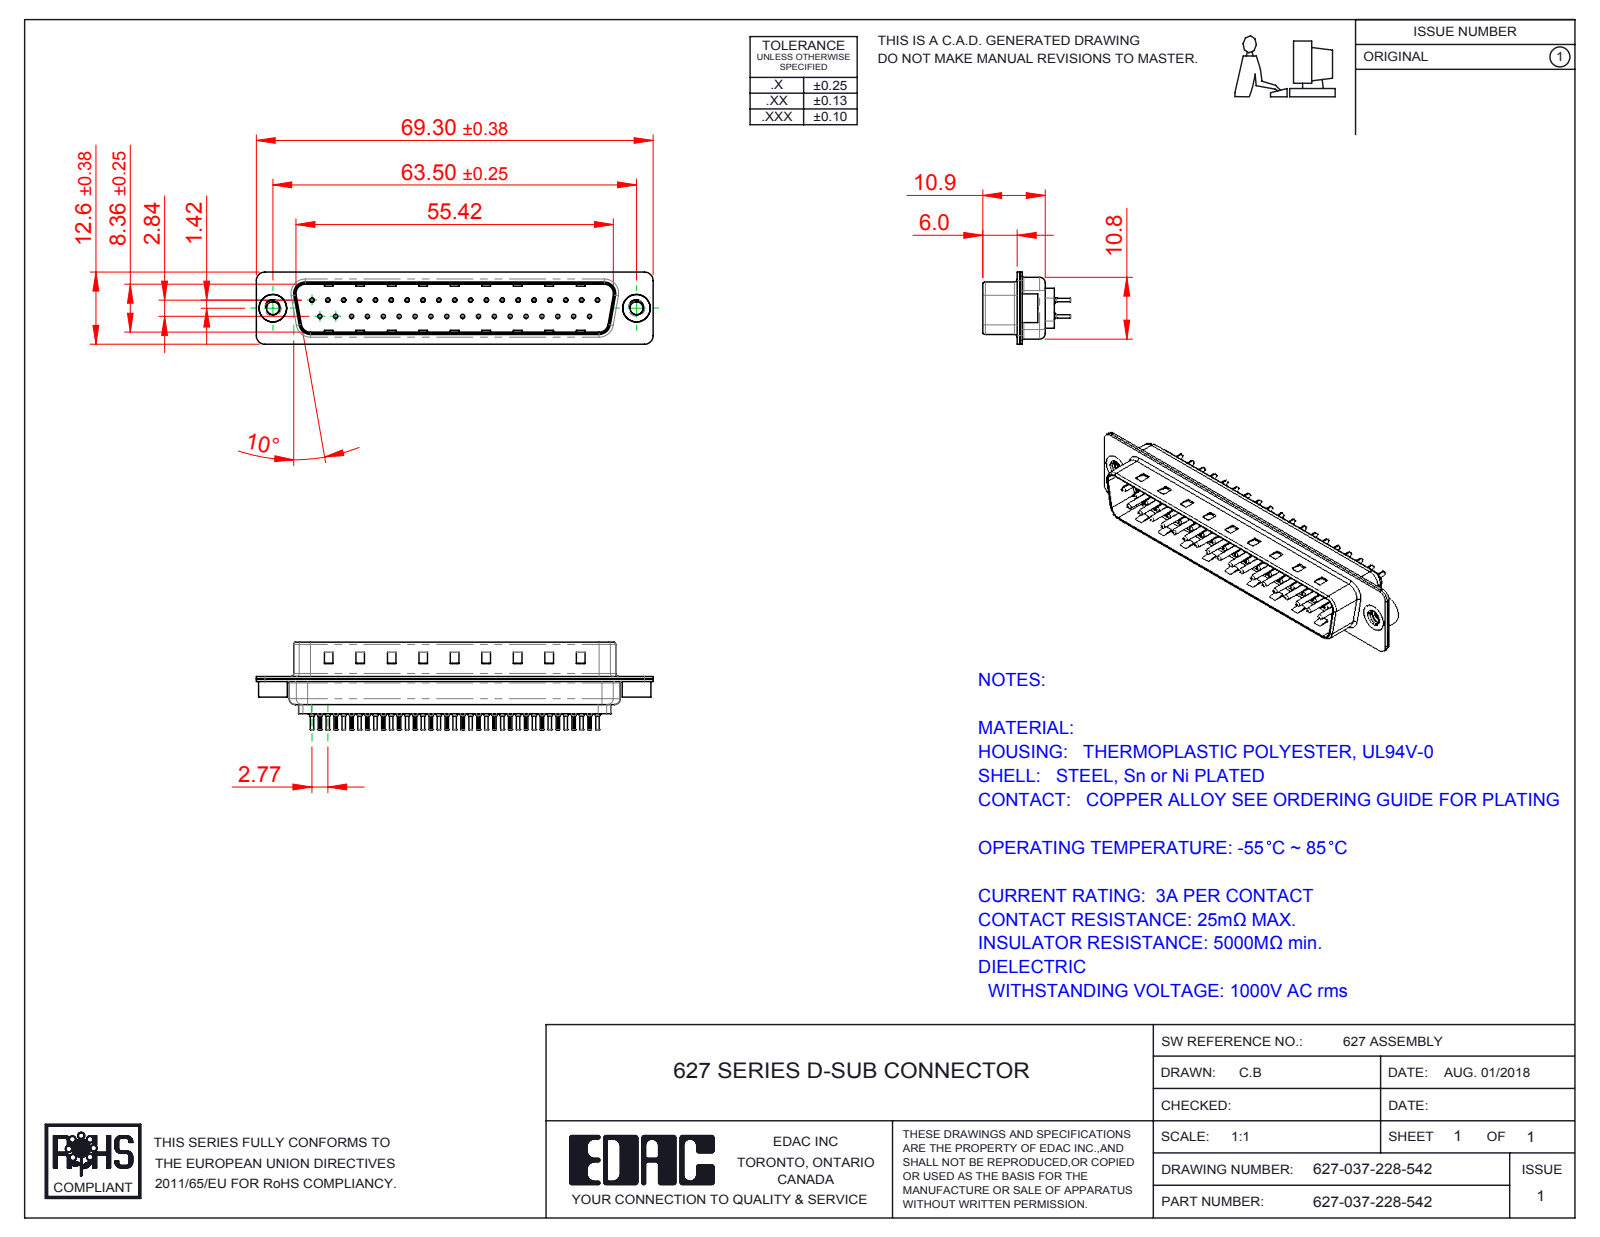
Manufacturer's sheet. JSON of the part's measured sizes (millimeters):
{"part_name": "627 Contact Row 2_28L; 627 Contact Row 1_28L; 627 4-40 Threaded Rivet; 627 Shell Rear_37 Contacts (+3 more)", "step_written_by": "SolidWorks 2016 (CONFIG_CONTROL_DESIGN)", "units": "millimeters", "bodies": {"solids": 42, "faces": 4038, "planar": 1091, "cylindrical": 1510, "other": 1437}, "overall_size": [69.3, 15.3, 12.6], "volume_mm3": 3685, "surface_area_mm2": 10474, "round_holes": [[0.2, 37], [0.35, 37], [1.1, 37], [1.6, 37], [2.26, 2], [4, 2], [4.8, 2]], "round_bosses_or_shafts": [[2, 37], [1.5, 37], [0.75, 37], [0.6, 37], [5, 2], [4.9, 2]], "partial_cylinders_radius": [[0.1, 74], [1.5, 16], [2, 12], [0.5, 8], [1.6, 8], [0.25, 4], [0.6, 4], [0.65, 4]], "face_to_face_distances": [0.4, 0.82, 9.58, 0.45, 8.76, 1.5, 0.9, 1.4, 6.05, 0.42], "hole_center_spacings": [3.16, 2.77, 5.54, 8.31, 5.04, 10.1, 11.08, 12.78]}
